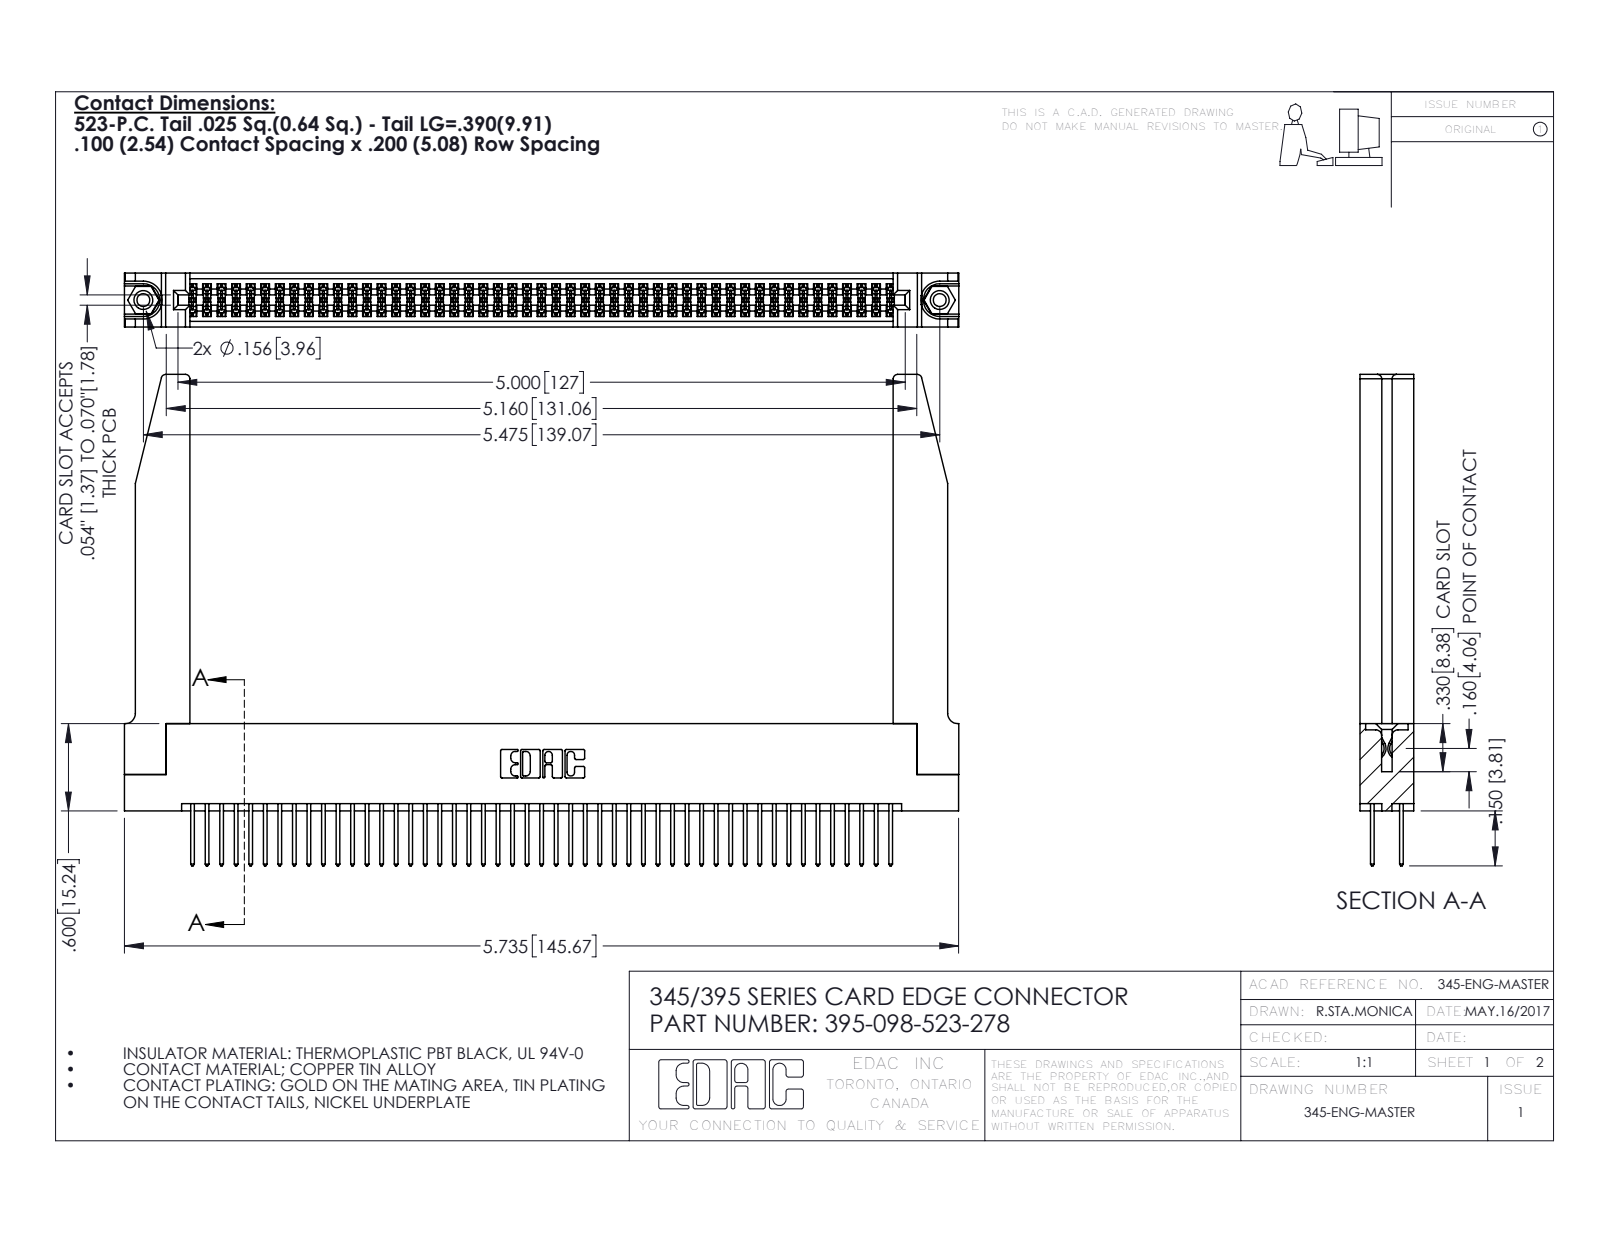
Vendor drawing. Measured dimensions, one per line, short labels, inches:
name: 395-098-523-278; 345-220-078_345-220-078; 345-292-001_345-293-123; 345-250-001_345-250-001-102 (+1 more)
written by: SolidWorks 2016 (CONFIG_CONTROL_DESIGN)
unit: in
bodies: 103 solids, 5260 faces (3456 planar, 1752 cylindrical, 52 other)
size: 5.736 × 3.377 × 0.37
volume: 1.354 in³; area: 45.24 in²
holes: 2× ⌀0.089, 2× ⌀0.125, 2× ⌀0.156, 1× ⌀0.064
bosses: 2× ⌀0.155
rounds: 147× R0.006, 98× R0.01, 22× R0.01, 8× R0.03, 6× R0.007, 6× R0.031, 3× R0.026, 2× R0.014
face distances: 0.072, 0.298, 0.37, 0.2, 0.098, 0.272, 0.025, 0.225, 0.175, 0.148
hole spacings: 0.27, 5.239, 5.475
